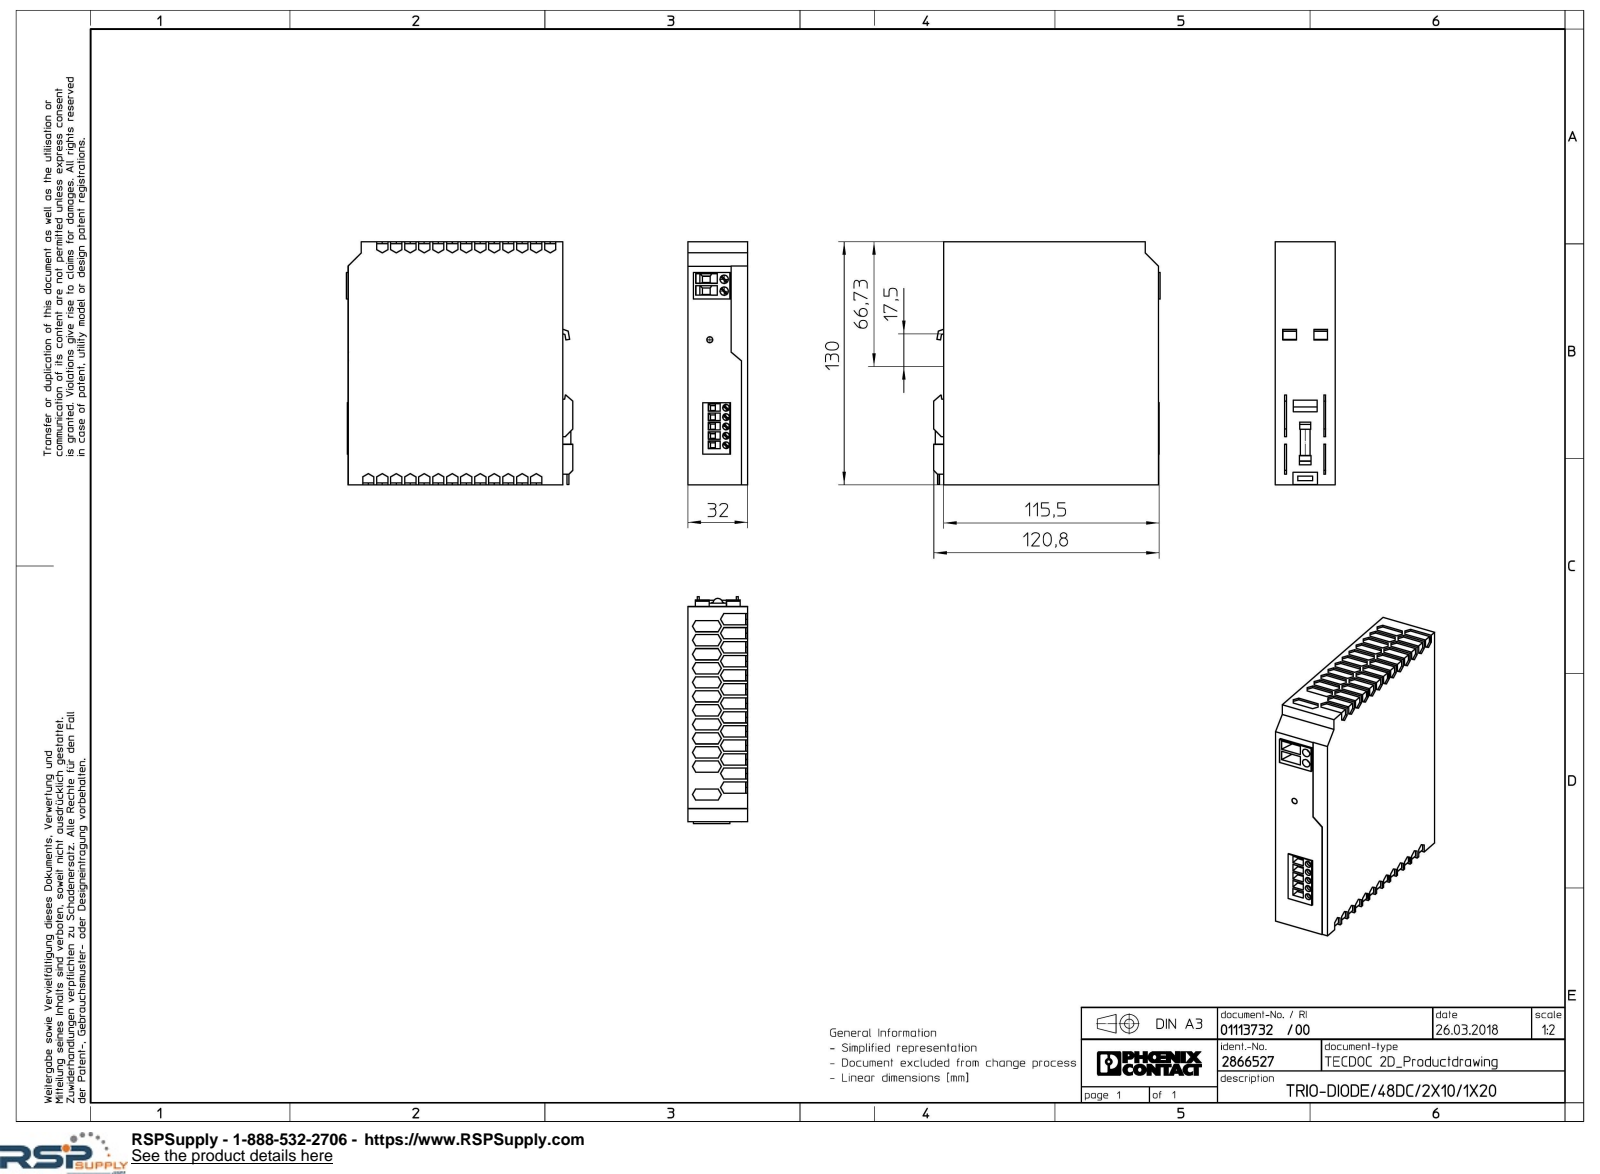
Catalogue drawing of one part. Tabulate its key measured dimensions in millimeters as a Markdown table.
| quantity | value |
| --- | --- |
| part name | TRIO_DIODE_48DC_2X10_1X20-select |
| STEP written by | Creo Elements/Direct Modeling 18.1I 14-Aug-2016 (C) Parametric Technology GmbH (AUTOMOTIVE_DESIGN) |
| units | millimeters |
| bodies | 1 solid, 636 faces (617 planar, 19 cylindrical, 0 other) |
| overall size | 130 × 121.3 × 32 |
| volume | 471 008 mm³ |
| surface area | 50 707 mm² |
| round holes (diameter × count) | 3.6 × 4, 4.5 × 2, 3.2 × 1, 3.55 × 1 |
| partial cylindrical surfaces (radius × count) | 2.48 × 2, 2.6 × 1 |
| main face-to-face distances | 32, 1, 129, 115.1, 128, 130, 5, 114.9, 31, 7.5 |
| hole center spacings | 5, 10, 15, 6.35, 20, 27.12, 33.25, 37.37 |
